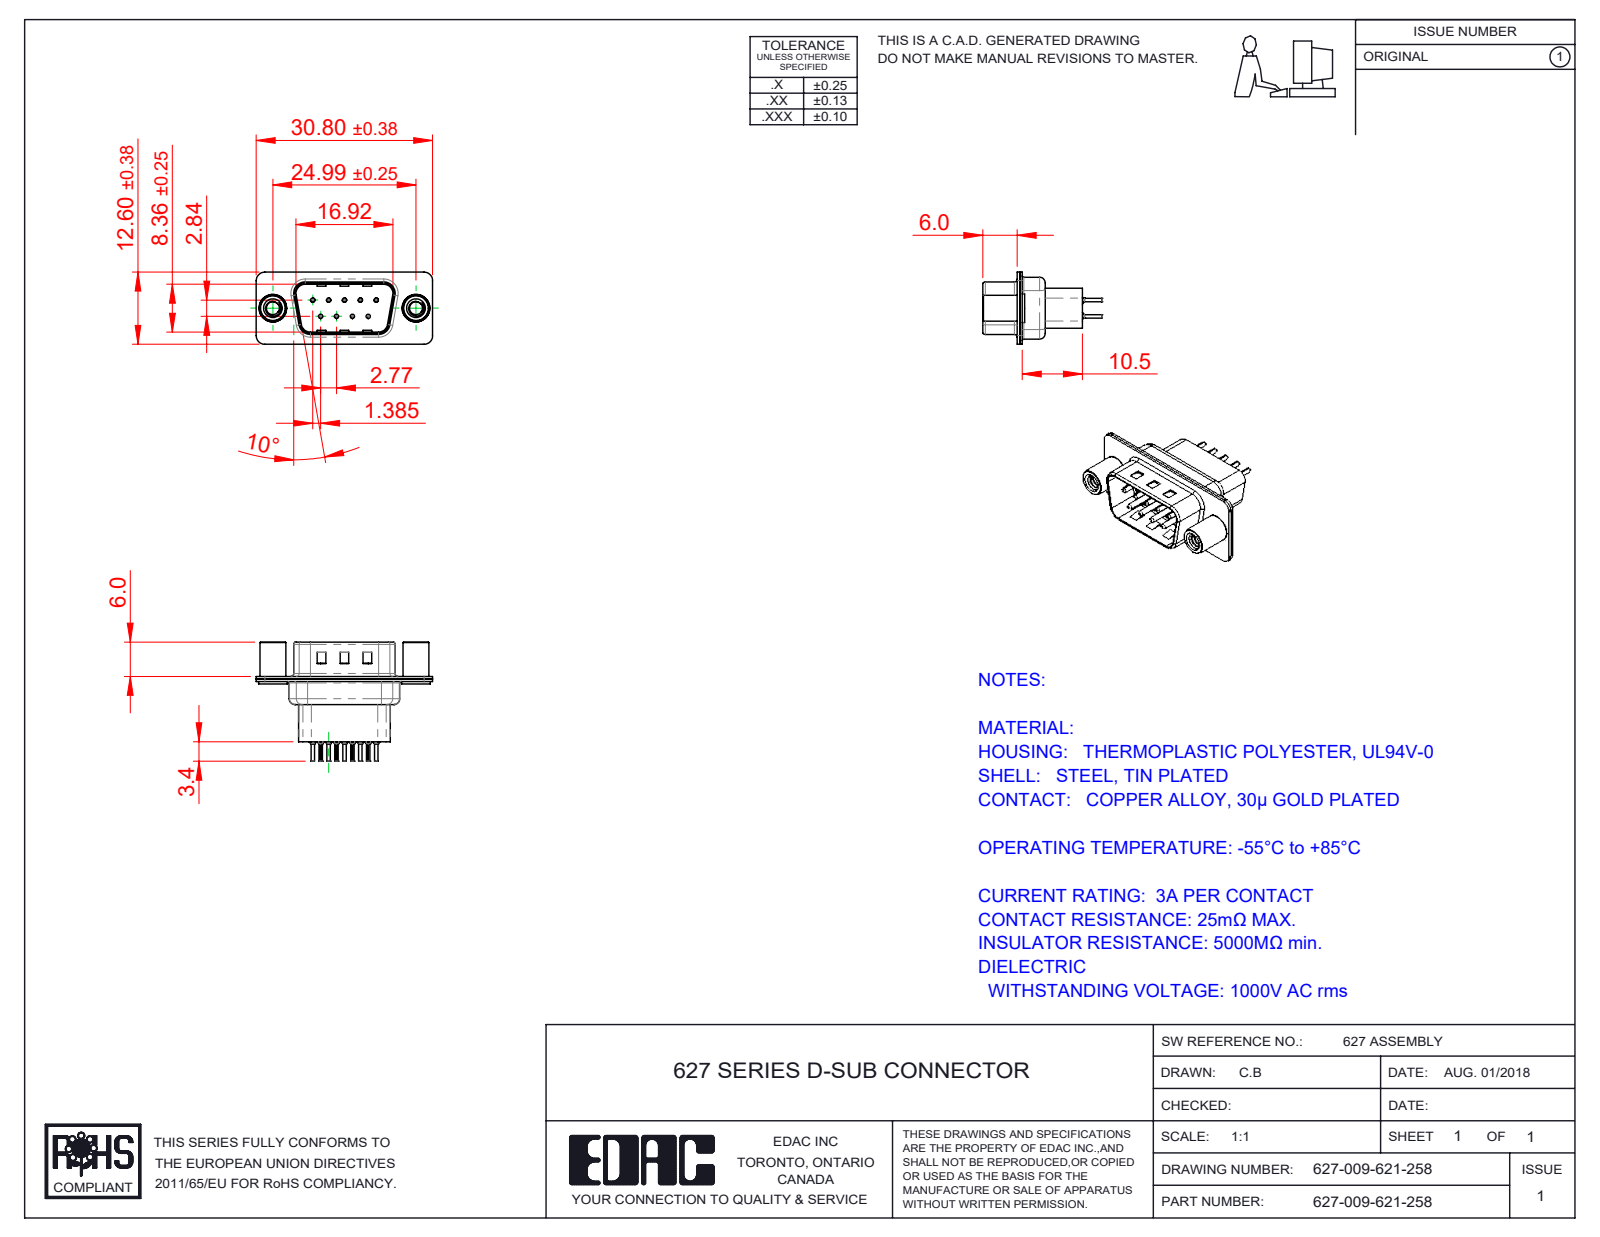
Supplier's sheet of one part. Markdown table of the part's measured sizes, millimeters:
| quantity | value |
| --- | --- |
| part name | 627 Contact Row 1_21H; 627 Contact Row 2_21H; 627 Shell Front_09 Contacts; 627 4-40 Threaded Standoff (+3 more) |
| STEP written by | SolidWorks 2020 (CONFIG_CONTROL_DESIGN) |
| units | millimeters |
| bodies | 14 solids, 1220 faces (325 planar, 490 cylindrical, 405 other) |
| overall size | 30.8 × 20.8 × 12.6 |
| volume | 1 835 mm³ |
| surface area | 4 894 mm² |
| round holes (diameter × count) | 0.2 × 9, 0.35 × 9, 1.1 × 9, 1.6 × 9, 2.26 × 2, 4 × 2, 4.8 × 2 |
| round bosses / shafts (diameter × count) | 2 × 9, 1.5 × 9, 0.75 × 9, 0.6 × 9, 5 × 2, 4.9 × 2, 4.5 × 2 |
| partial cylindrical surfaces (radius × count) | 0.1 × 18, 1.5 × 18, 2 × 12, 0.5 × 8, 1.6 × 8, 0.25 × 4, 0.6 × 4, 0.65 × 4 |
| main face-to-face distances | 0.4, 0.45, 0.9, 0.82, 9.58, 1.4, 1.5, 0.68, 7.68, 1.08 |
| hole center spacings | 3.16, 2.77, 5.54, 5.03, 5.04, 8.31, 7.48, 7.49 |
